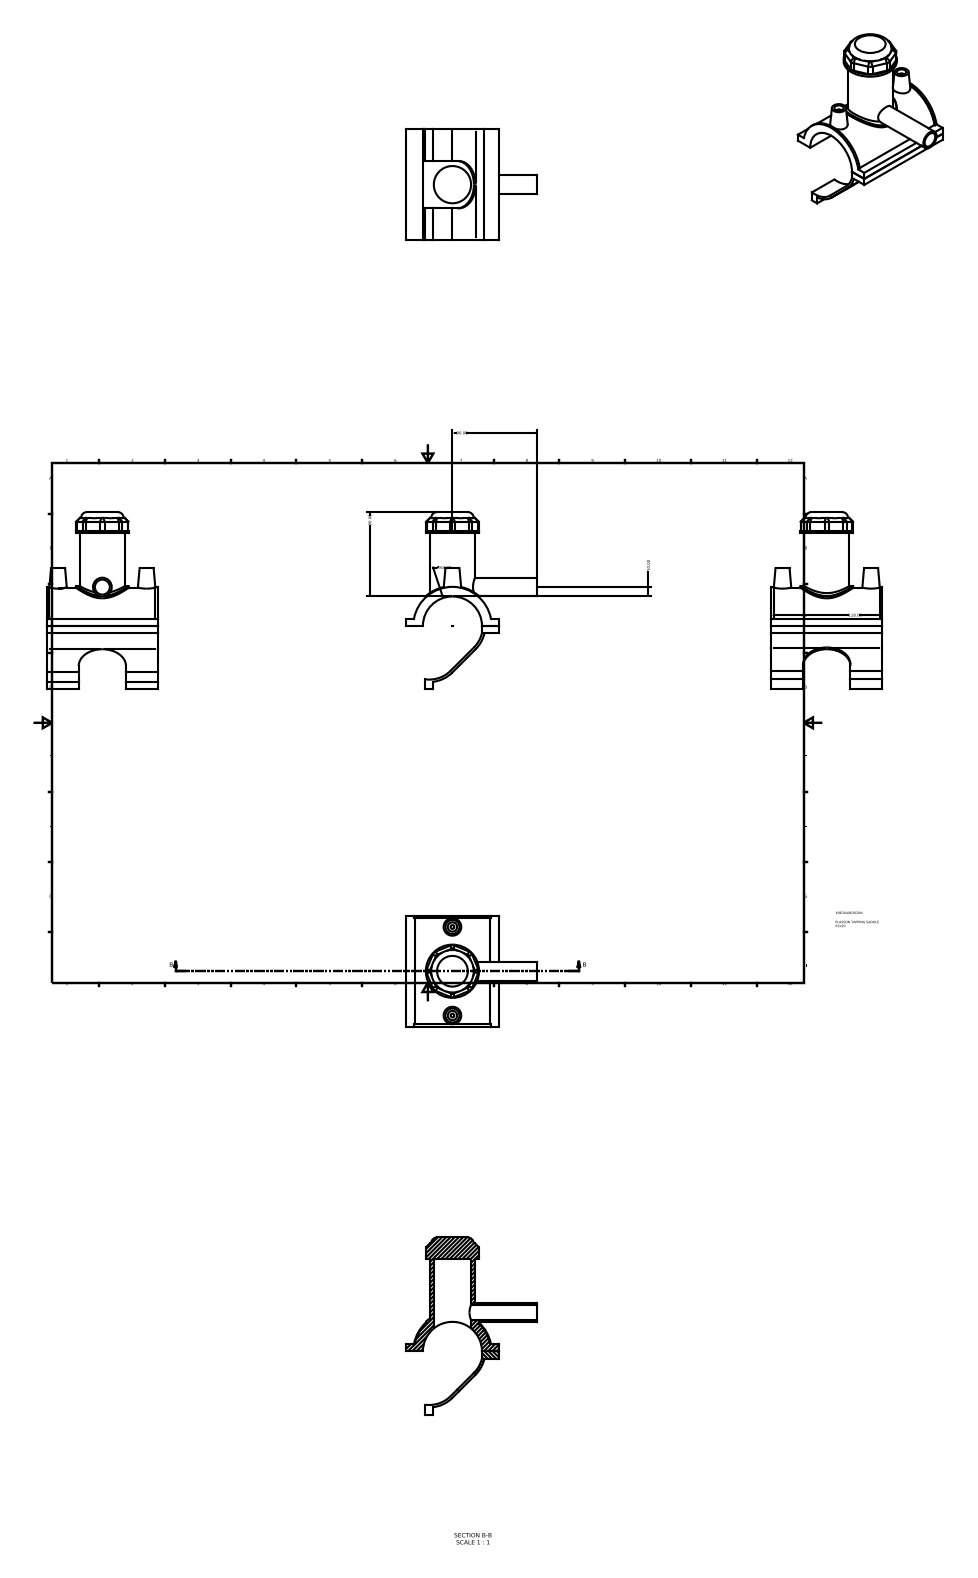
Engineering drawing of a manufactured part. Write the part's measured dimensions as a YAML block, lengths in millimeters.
part_name: "496304063020N"
step_written_by: "Autodesk Inventor 2015 (AUTOMOTIVE_DESIGN)"
units: millimeters
bodies: {solids: 2, faces: 105, planar: 63, cylindrical: 30, other: 12}
overall_size: [188.78, 140, 118]
volume: 267725
surface_area: 91493
round_holes:
  - {diameter: 10, count: 2}
  - {diameter: 16, count: 1}
  - {diameter: 39.69, count: 1}
round_bosses_or_shafts:
  - {diameter: 4, count: 2}
  - {diameter: 56.7, count: 1}
  - {diameter: 48.2, count: 1}
  - {diameter: 20, count: 1}
partial_cylinders:
  - {radius: 6.3, count: 8}
  - {radius: 32.38, count: 2}
  - {radius: 34.98, count: 2}
  - {radius: 25.2, count: 1}
  - {radius: 31.5, count: 1}
  - {radius: 40.95, count: 1}
  - {radius: 41.77, count: 1}
  - {radius: 42.59, count: 1}
face_to_face_distances: [7.82, 2.6, 98.95, 106.77, 118, 7.83, 15.65, 91.12, 15.64, 91.13]
hole_center_spacings: [47.2, 94.4]
